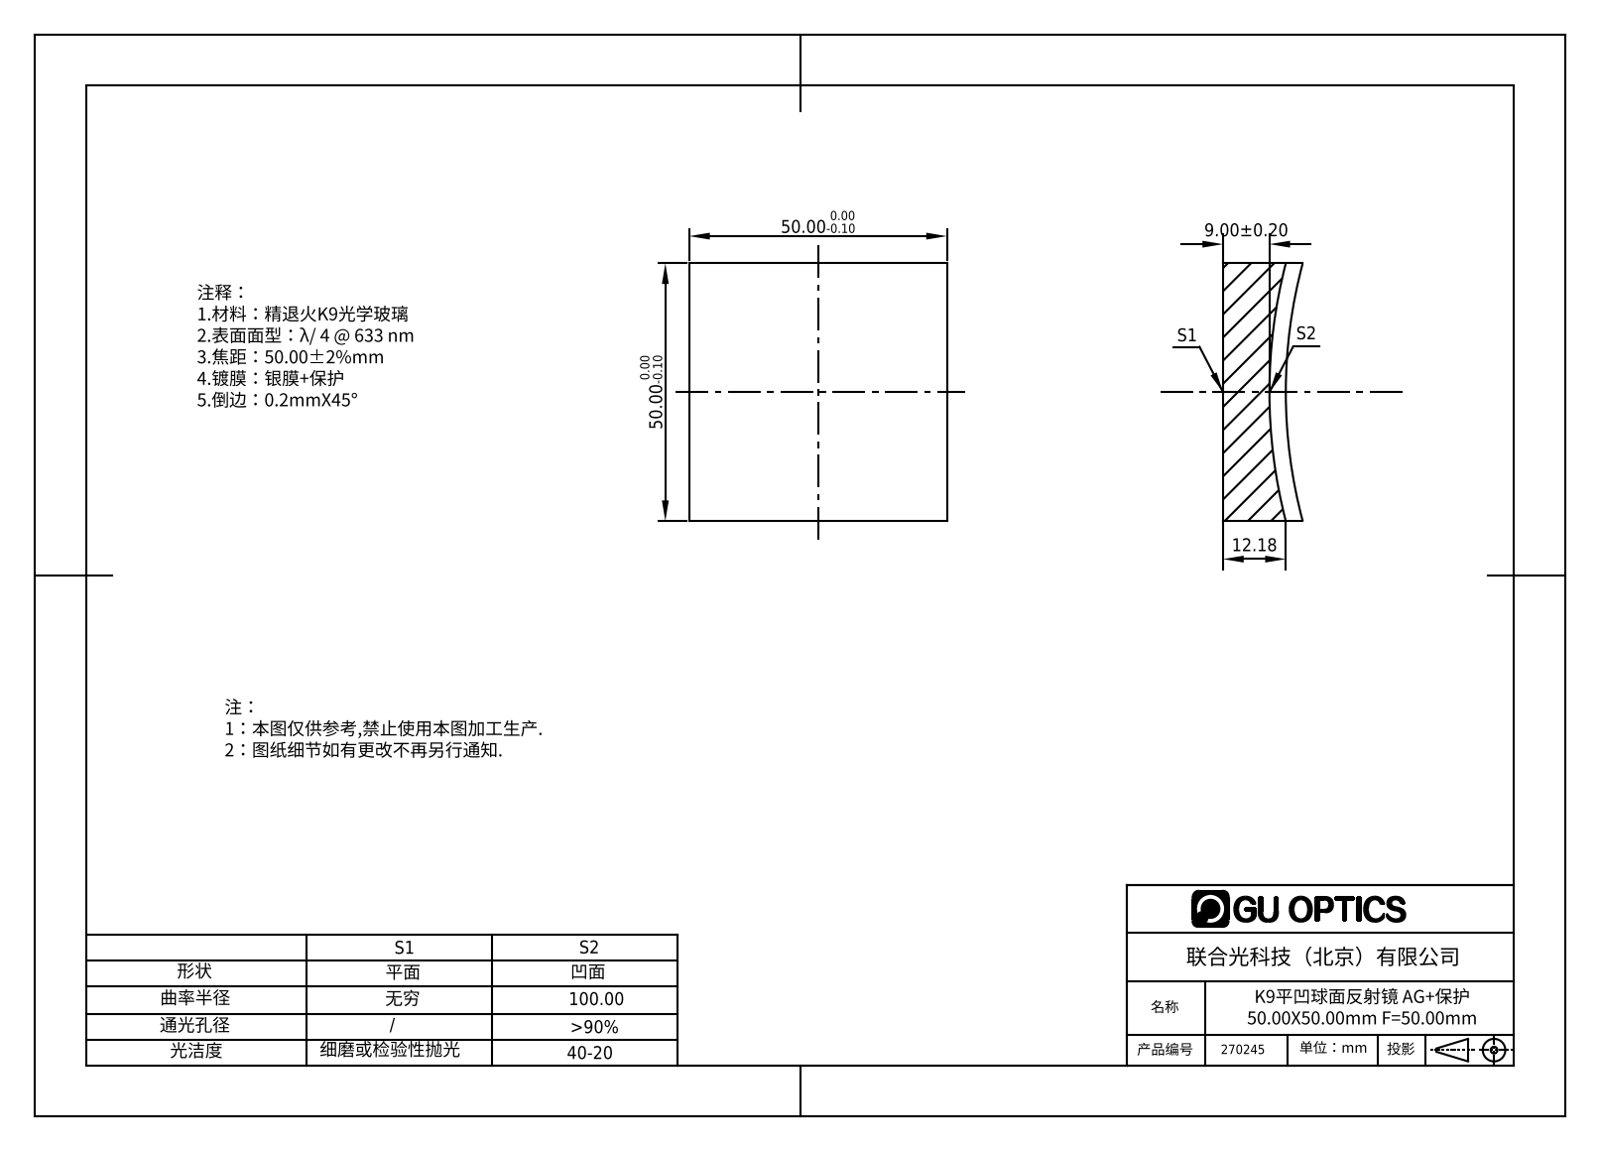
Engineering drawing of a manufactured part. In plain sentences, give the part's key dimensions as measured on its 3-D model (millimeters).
The part is named "270050". Its 3-D file was written by "SolidWorks 2019 (AUTOMOTIVE_DESIGN)". It is 1 solid with 7 faces: 5 planar, 0 cylindrical and 2 other. Overall it measures 50 by 50 by 15.46 millimeters. Its volume is 27 787 cubic millimeters and its surface area 7 707 square millimeters. The main face-to-face distances are 50.
